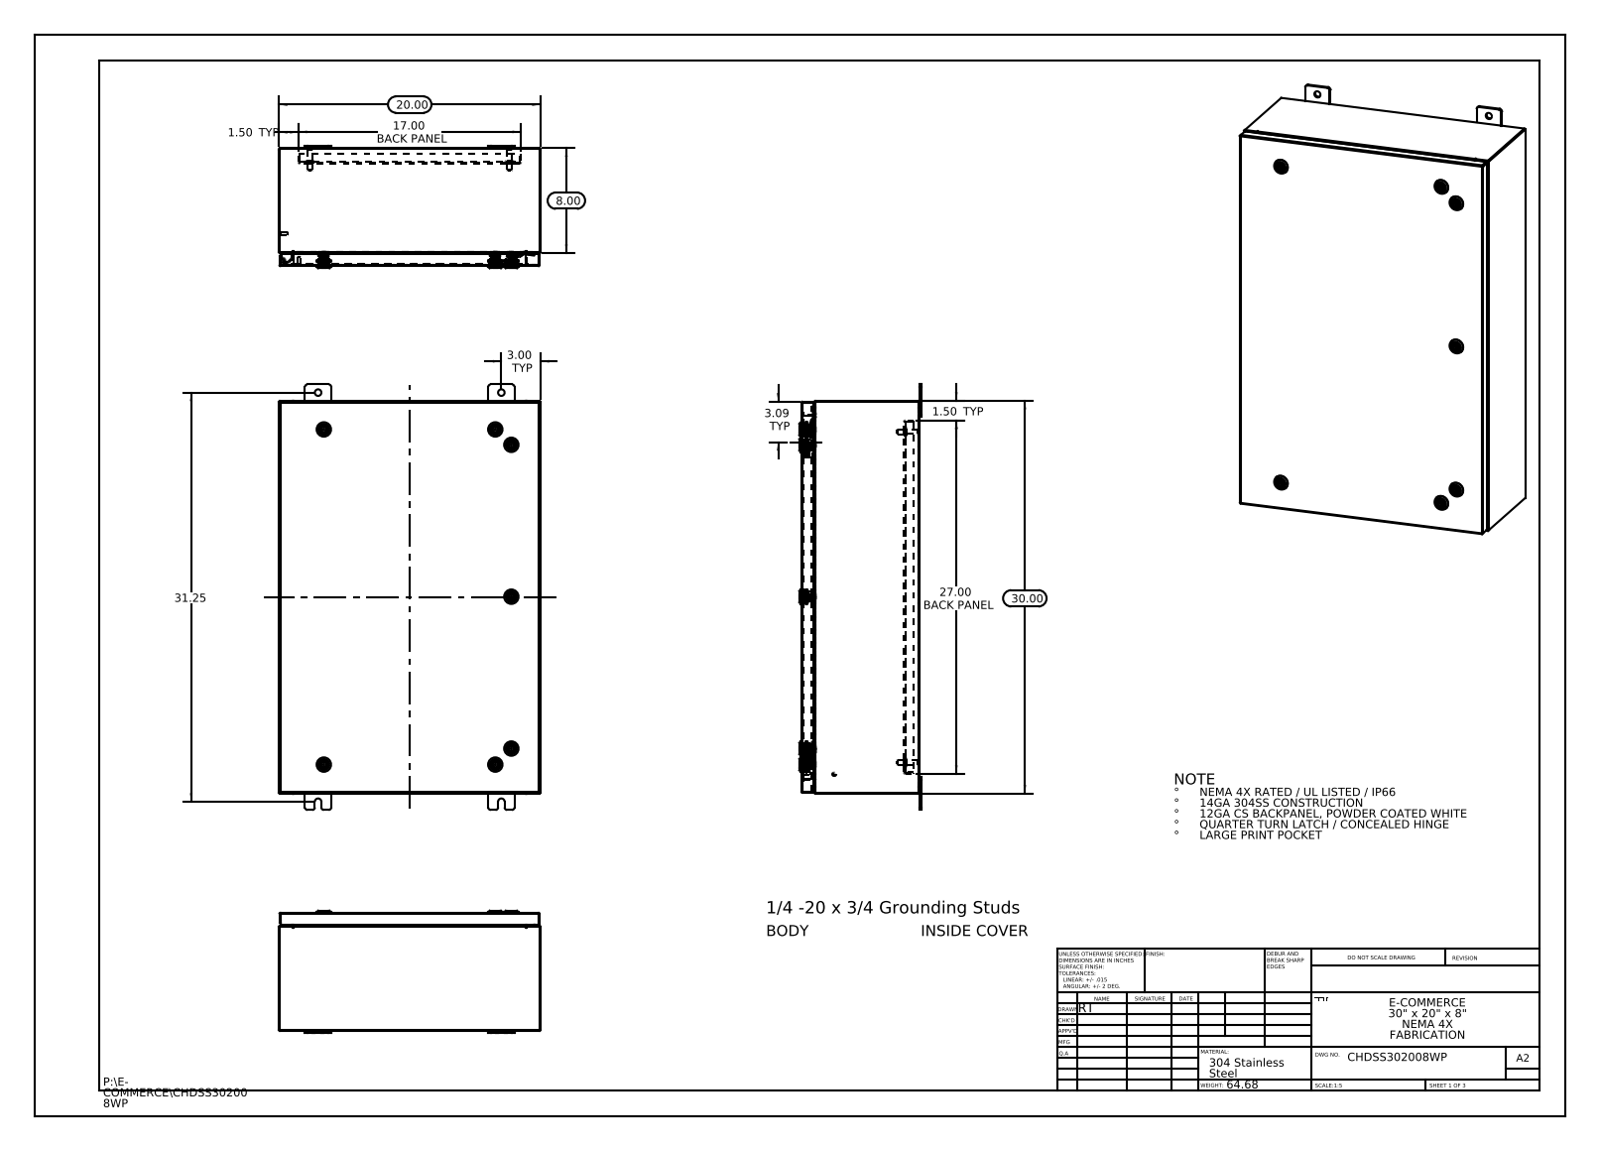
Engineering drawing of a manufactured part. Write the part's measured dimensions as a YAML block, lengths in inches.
part_name: "CHDSS302008WP Bottom; CHDSS302008WP Mounting Studs; Concealed Hinge (Cover Side); HW-CLH-R001-0500_2412-026240-2445-Industrilas (+8 more)"
step_written_by: "SolidWorks 2013 (CONFIG_CONTROL_DESIGN)"
units: inches
bodies: {solids: 60, faces: 6230, planar: 1808, cylindrical: 1940, other: 2482}
overall_size: [32.5, 20, 9.356]
volume: 230.8
surface_area: 5739
round_holes:
  - {diameter: 0.5, count: 8}
  - {diameter: 0.197, count: 7}
  - {diameter: 0.394, count: 7}
  - {diameter: 0.4, count: 7}
  - {diameter: 0.63, count: 7}
  - {diameter: 0.787, count: 7}
  - {diameter: 0.136, count: 4}
  - {diameter: 0.211, count: 1}
round_bosses_or_shafts:
  - {diameter: 0.236, count: 9}
  - {diameter: 1.102, count: 7}
  - {diameter: 0.78, count: 7}
  - {diameter: 0.626, count: 7}
  - {diameter: 0.61, count: 7}
  - {diameter: 0.531, count: 7}
  - {diameter: 0.392, count: 7}
  - {diameter: 0.114, count: 7}
partial_cylinders:
  - {radius: 0.006, count: 231}
  - {radius: 0.118, count: 231}
  - {radius: 0.028, count: 84}
  - {radius: 0.02, count: 28}
  - {radius: 0.197, count: 28}
  - {radius: 0.19, count: 24}
  - {radius: 0.013, count: 22}
  - {radius: 0.088, count: 18}
face_to_face_distances: [0.075, 0.074, 9.01, 8.935, 8.936, 8.861, 0.104, 19.925, 1, 1.075]
hole_center_spacings: [1.858, 3.065, 11.6, 13.1, 14, 15.25, 25.25, 25.6]
